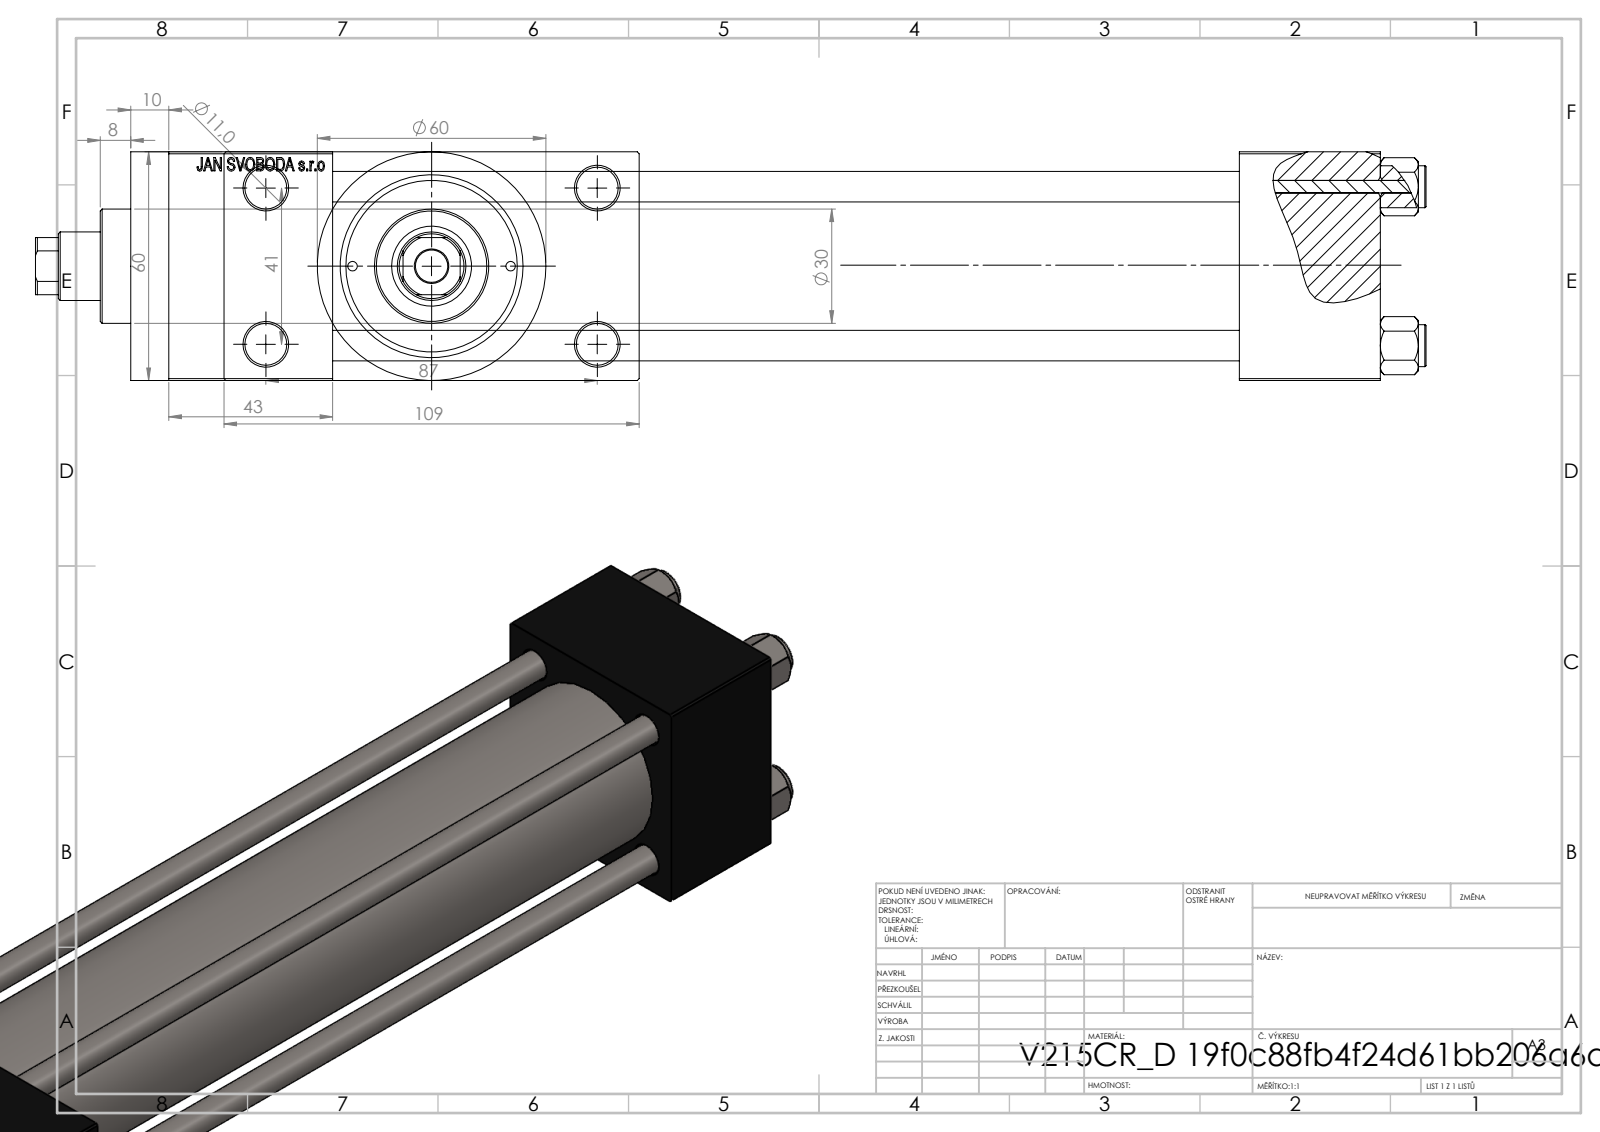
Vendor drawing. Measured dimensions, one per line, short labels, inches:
name: NUT_M5_D; V215CR_VCP_D; V215CR_D_Body; V215_VC_A (+1 more)
written by: SolidWorks 2019 (CONFIG_CONTROL_DESIGN)
unit: in
bodies: 11 solids, 1112 faces (500 planar, 92 cylindrical, 520 other)
size: 14.37 × 4.291 × 2.362
volume: 40.72 in³; area: 309.1 in²
holes: 4× ⌀0.315, 4× ⌀0.433, 2× ⌀0.098, 2× ⌀0.276, 2× ⌀0.656, 2× ⌀0.945, 1× ⌀0.335, 1× ⌀0.709, 1× ⌀0.827, 1× ⌀1.22, 1× ⌀1.575, 1× ⌀1.772
bosses: 4× ⌀0.433, 1× ⌀2.362, 1× ⌀1.811, 1× ⌀1.181
rounds: 1× R0.335
face distances: 2.362, 9.37, 0.965, 3.327, 1.457, 10.827, 12.52, 11.063, 1.693, 11.21
hole spacings: 0.821, 0.892, 1.161, 1.206, 1.642, 1.832, 1.856, 1.893
